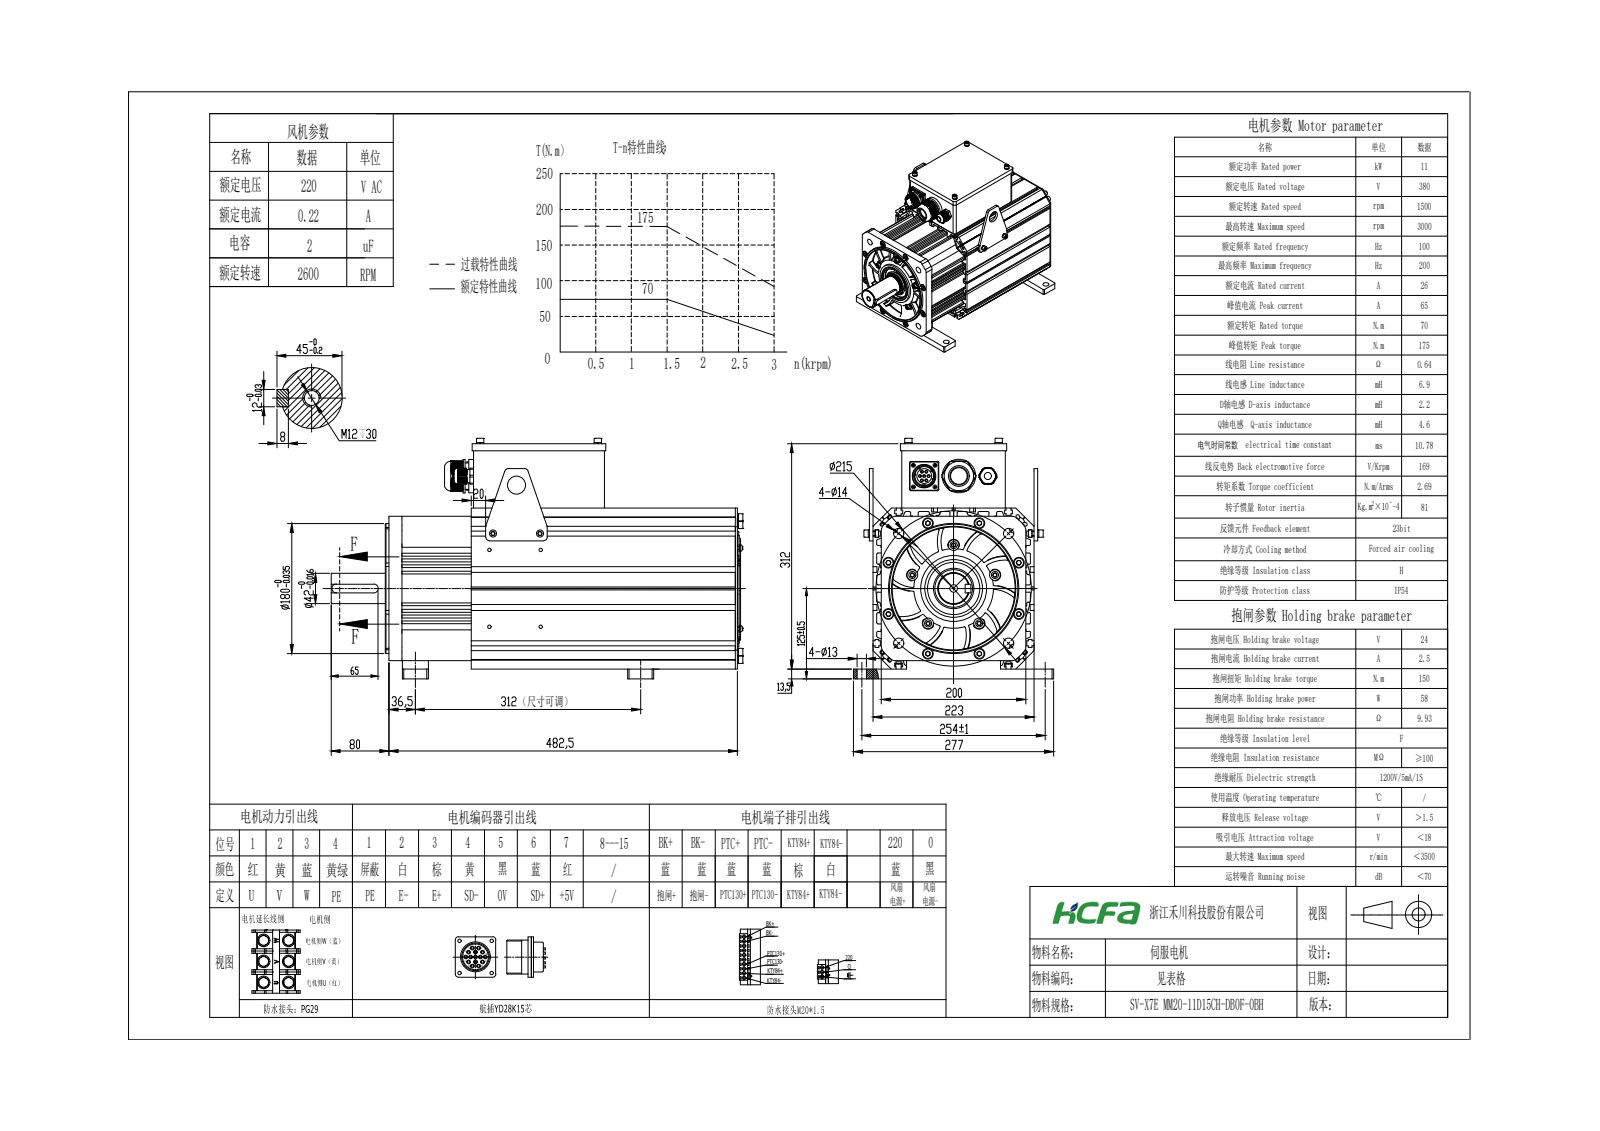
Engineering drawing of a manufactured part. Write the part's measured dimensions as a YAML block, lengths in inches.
part_name: "11KW抱闸"
step_written_by: "SolidWorks 2021 (CONFIG_CONTROL_DESIGN)"
units: inches
bodies: {solids: 91, faces: 4316, planar: 2345, cylindrical: 1227, other: 744}
overall_size: [22.445, 13.114, 10.906]
volume: 373.8
surface_area: 3706
round_holes:
  - {diameter: 0.197, count: 24}
  - {diameter: 0.268, count: 17}
  - {diameter: 0.263, count: 15}
  - {diameter: 0.354, count: 14}
  - {diameter: 0.256, count: 11}
  - {diameter: 0.591, count: 10}
  - {diameter: 0.138, count: 8}
  - {diameter: 0.315, count: 8}
  - {diameter: 0.165, count: 7}
  - {diameter: 0.177, count: 6}
  - {diameter: 0.551, count: 5}
  - {diameter: 0.098, count: 4}
round_bosses_or_shafts:
  - {diameter: 0.079, count: 24}
  - {diameter: 0.394, count: 17}
  - {diameter: 0.236, count: 17}
  - {diameter: 0.389, count: 15}
  - {diameter: 0.315, count: 14}
  - {diameter: 0.157, count: 11}
  - {diameter: 0.512, count: 10}
  - {diameter: 0.118, count: 8}
partial_cylinders:
  - {radius: 0.079, count: 84}
  - {radius: 0.02, count: 24}
  - {radius: 0.197, count: 20}
  - {radius: 0.118, count: 15}
  - {radius: 0.098, count: 14}
  - {radius: 0.394, count: 12}
  - {radius: 0.059, count: 8}
  - {radius: 0.095, count: 8}
face_to_face_distances: [8.78, 0.098, 0.197, 8.583, 0.256, 0.453, 8.327, 8.13, 0.315, 7.815]
hole_center_spacings: [4.035, 5.817, 4.189, 8.071, 0.07, 1.621, 1.689, 2.869]
